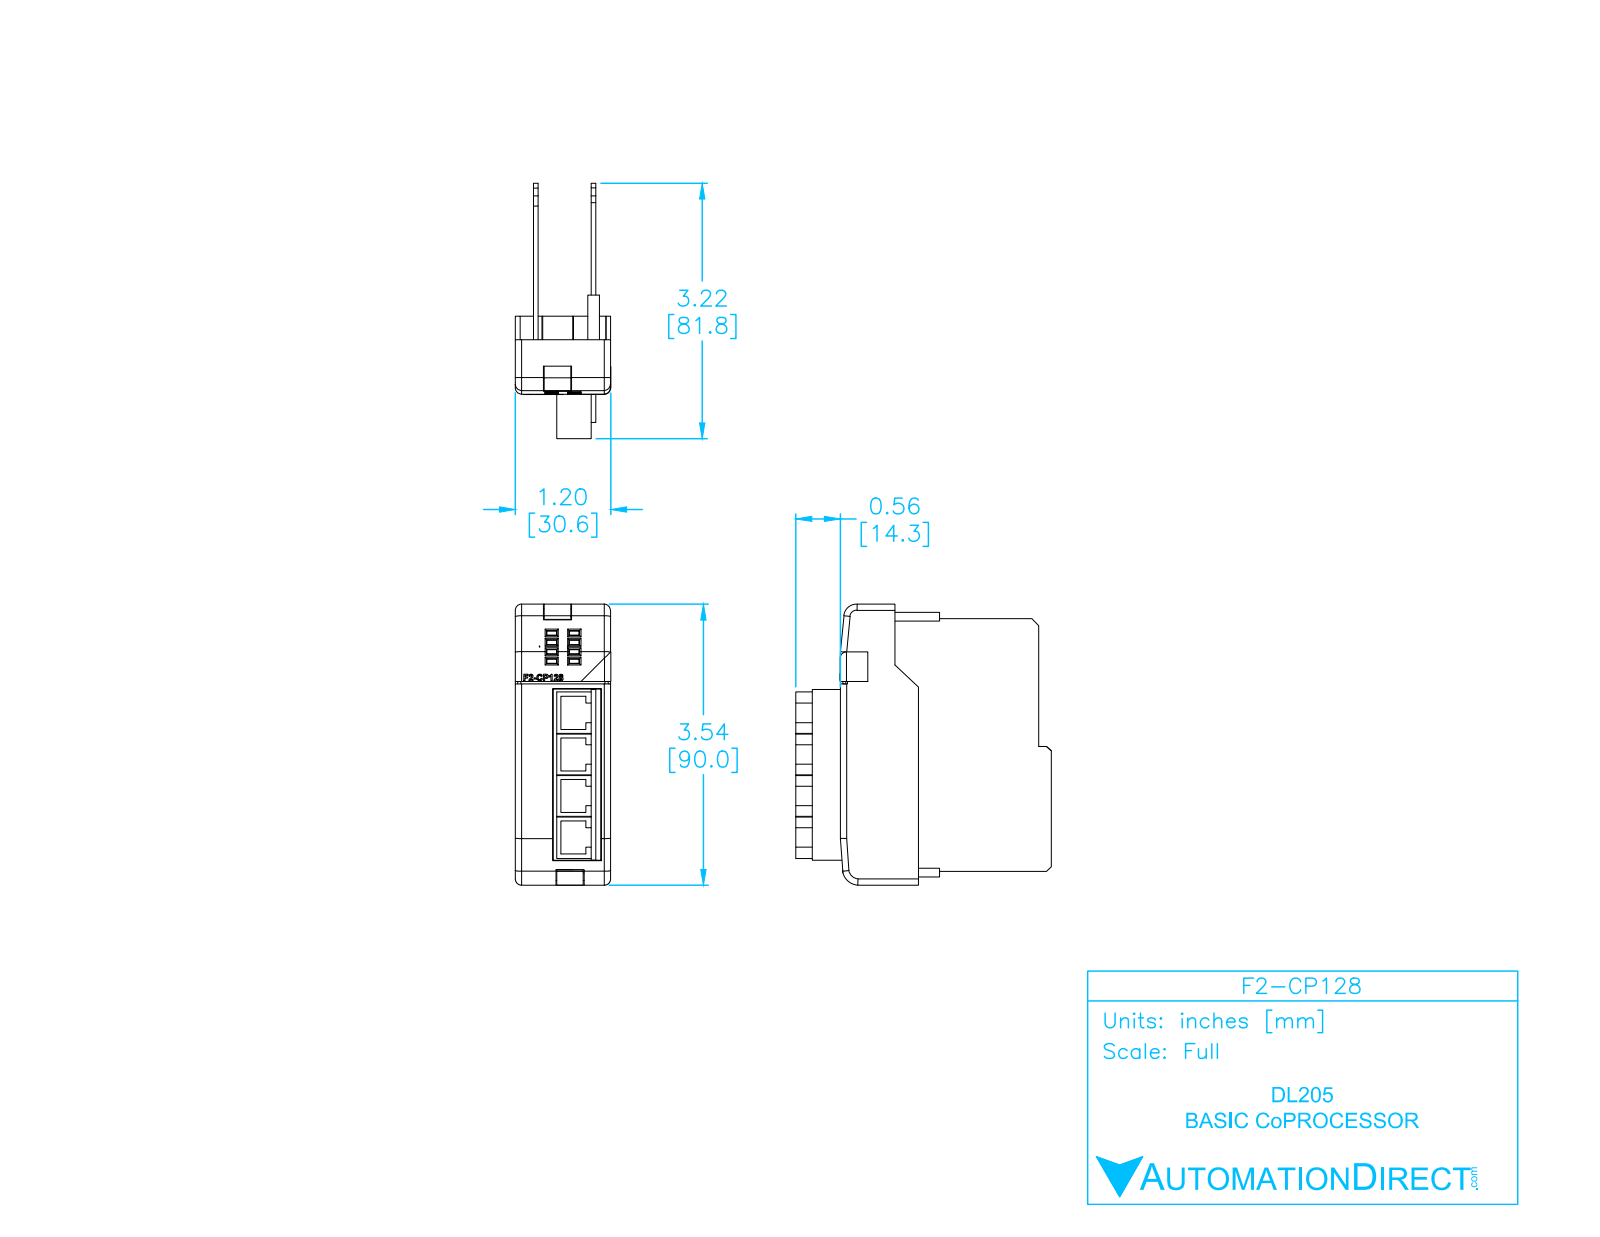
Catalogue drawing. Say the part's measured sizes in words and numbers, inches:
The part is named "F2-CP128". Its 3-D file was written by "SolidWorks 2009 (AUTOMOTIVE_DESIGN)". It is 6 solids with 430 faces: 284 planar, 84 cylindrical and 62 other. Overall it measures 3.543 by 3.222 by 1.203 inches. Its volume is 1.812 cubic inches and its surface area 65.4 square inches. Partial cylindrical surfaces (rounded edges, fillets, slot ends): 28 of radius 0.02, 11 of radius 0.079, 4 of radius 0.01, 2 of radius 0.039, 1 of radius 0.103, 1 of radius 0.149, 1 of radius 0.162, 1 of radius 0.208. The main face-to-face distances are 0.059, 0.728, 0.669, 0.787, 0.186, 0.914, 0.127, 0.855, 0.245, 0.973.
